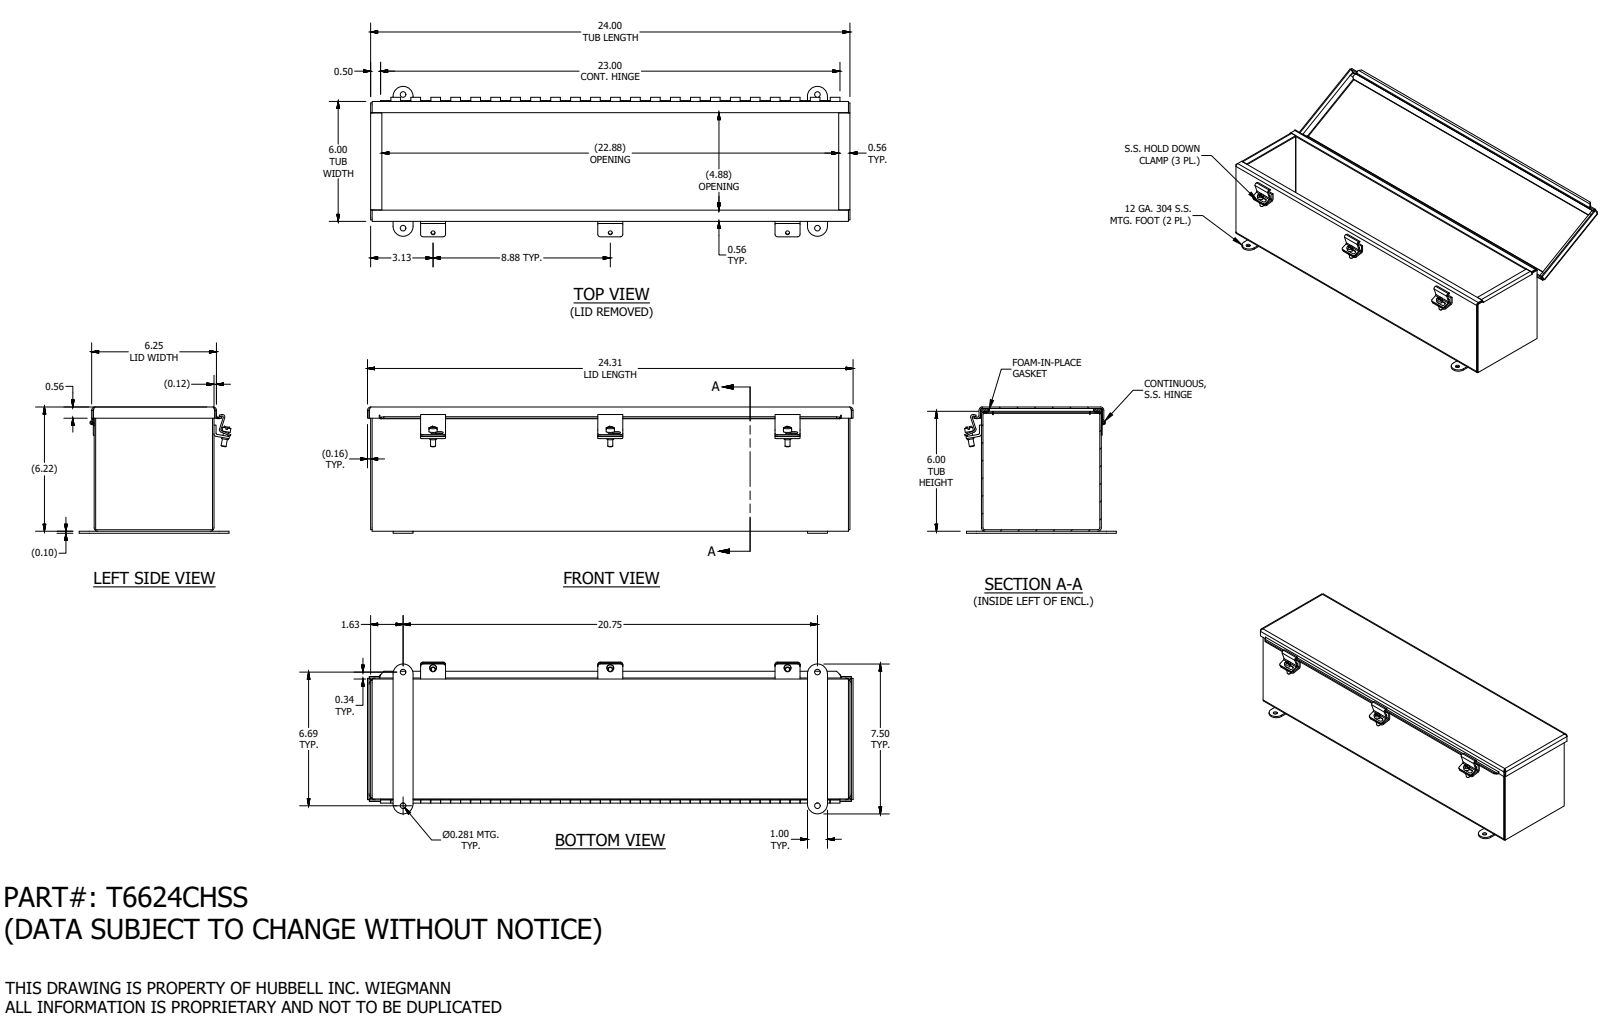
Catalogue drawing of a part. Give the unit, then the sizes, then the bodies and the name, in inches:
Units: inches
Overall size (bounding box): 24.313 × 7.598 × 6.322
Round holes (diameter × count): ⌀0.11 ×6, ⌀0.281 ×4, ⌀0.196 ×3, ⌀0.116 ×1
Round bosses / shafts (diameter × count): ⌀0.41 ×3, ⌀0.344 ×3, ⌀0.25 ×3, ⌀0.2 ×1, ⌀0.1 ×1
Partial cylindrical surfaces — rounded edges, fillets, slot ends (radius × count): R0.125 ×12, R0.094 ×11, R0.168 ×11, R0.085 ×8, R0.133 ×6, R0.242 ×4, R0.5 ×4, R0.063 ×3
Main face-to-face distances: 0.074, 5.926, 6.144, 6, 5.852, 6.218, 6.07, 23.926, 0.218, 23.852
Hole centre spacings: 8.875, 0.75, 6.687, 8.875, 17.75, 20.75, 21.801, 8.125
Volume: 61.22 in³ · Surface area: 1 628 in²
Bodies: 19 solids, 591 faces (355 planar, 197 cylindrical, 39 other)
Part name (STEP PRODUCT): T6624CHSS
STEP written by: SolidWorks 2019 (AUTOMOTIVE_DESIGN)
